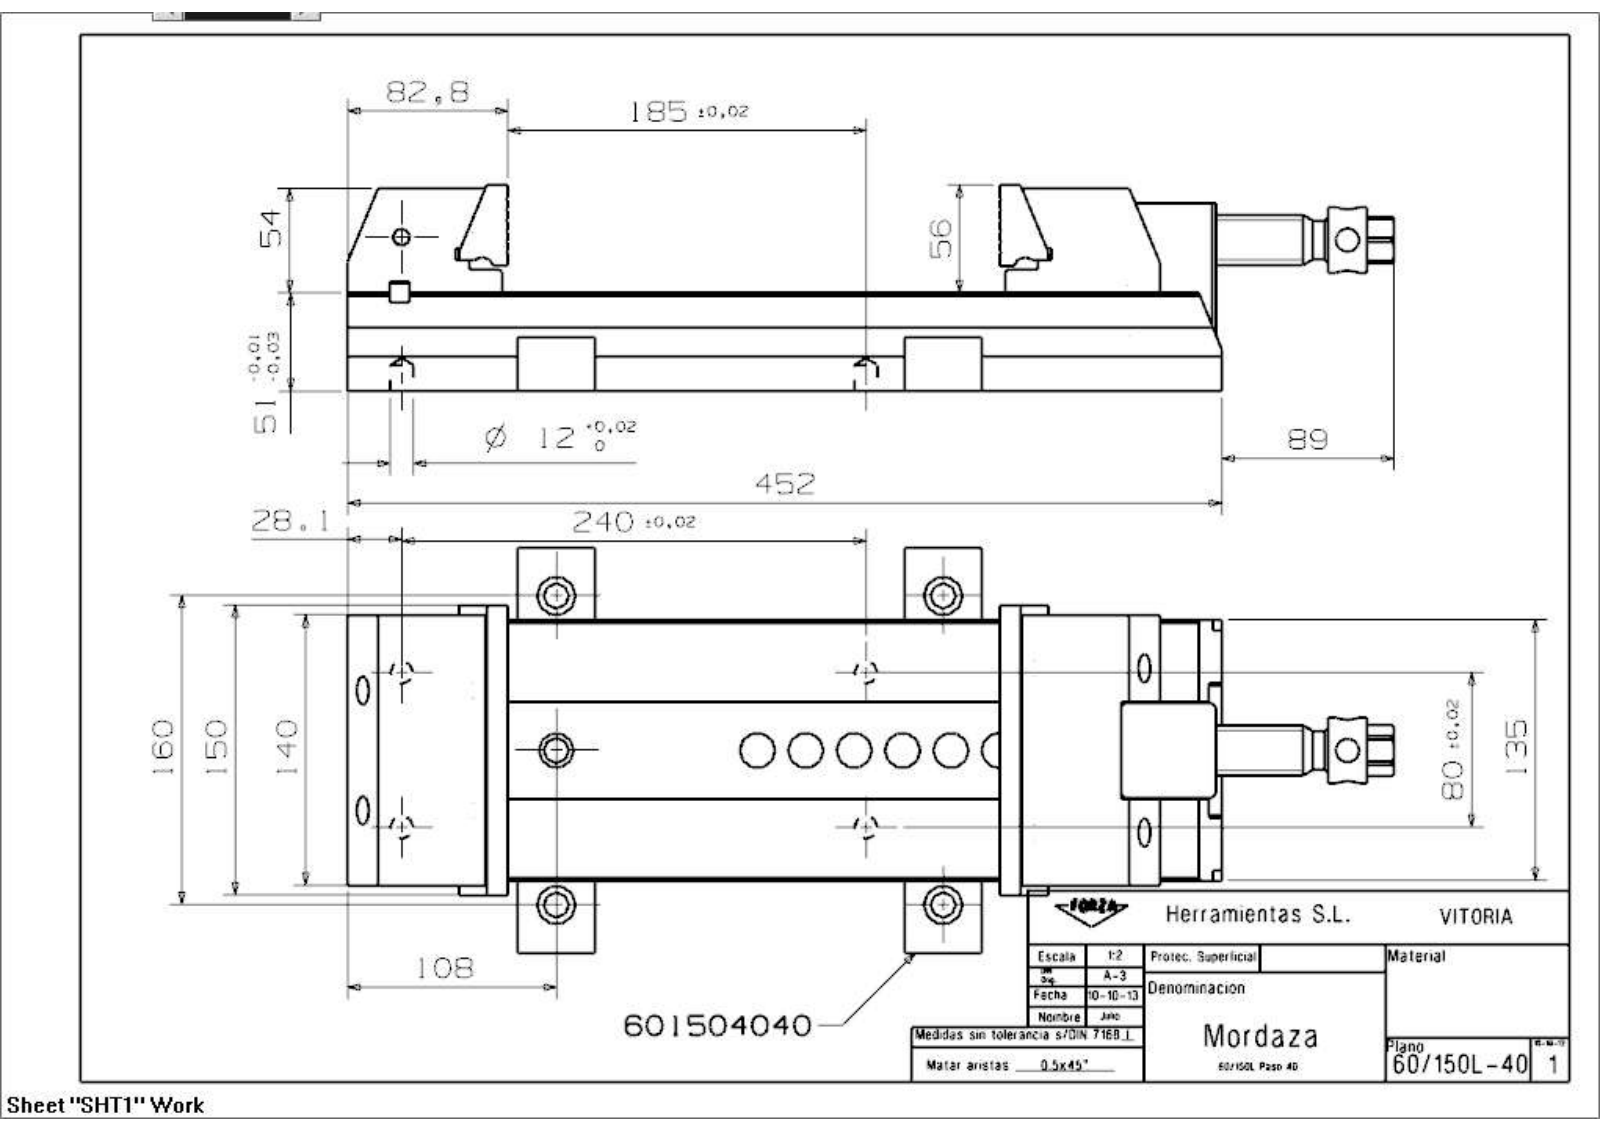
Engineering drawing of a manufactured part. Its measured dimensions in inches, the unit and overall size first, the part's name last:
Units: inches
Overall size (bounding box): 21.299 × 8.268 × 4.213
Round holes (diameter × count): ⌀0.512 ×9, ⌀0.472 ×6, ⌀0.591 ×6, ⌀0.787 ×5, ⌀0.275 ×4, ⌀0.335 ×4, ⌀0.346 ×4, ⌀0.394 ×4, ⌀0.417 ×4, ⌀0.748 ×4, ⌀0.487 ×2, ⌀0.866 ×2
Round bosses / shafts (diameter × count): ⌀1.339 ×1, ⌀1.331 ×1, ⌀1.024 ×1, ⌀0.787 ×1, ⌀0.65 ×1
Partial cylindrical surfaces — rounded edges, fillets, slot ends (radius × count): R0.059 ×4, R0.787 ×4, R0.063 ×2, R0.217 ×2, R0.236 ×2, R0.157 ×1, R0.354 ×1, R0.413 ×1
Main face-to-face distances: 2.008, 4.134, 0.76, 1.248, 1.378, 5.098, 1.063, 0.063, 0.697, 1.945
Hole centre spacings: 3.15, 3.747, 0.453, 2.894, 3.346, 3.518, 6.497, 0.455
Volume: 217.3 in³ · Surface area: 787 in²
Bodies: 16 solids, 467 faces (312 planar, 100 cylindrical, 55 other)
Part name (STEP PRODUCT): 60_150L_Mordaza
STEP written by: SIEMENS PLM Software NX 7.5 (CONFIG_CONTROL_DESIGN)
